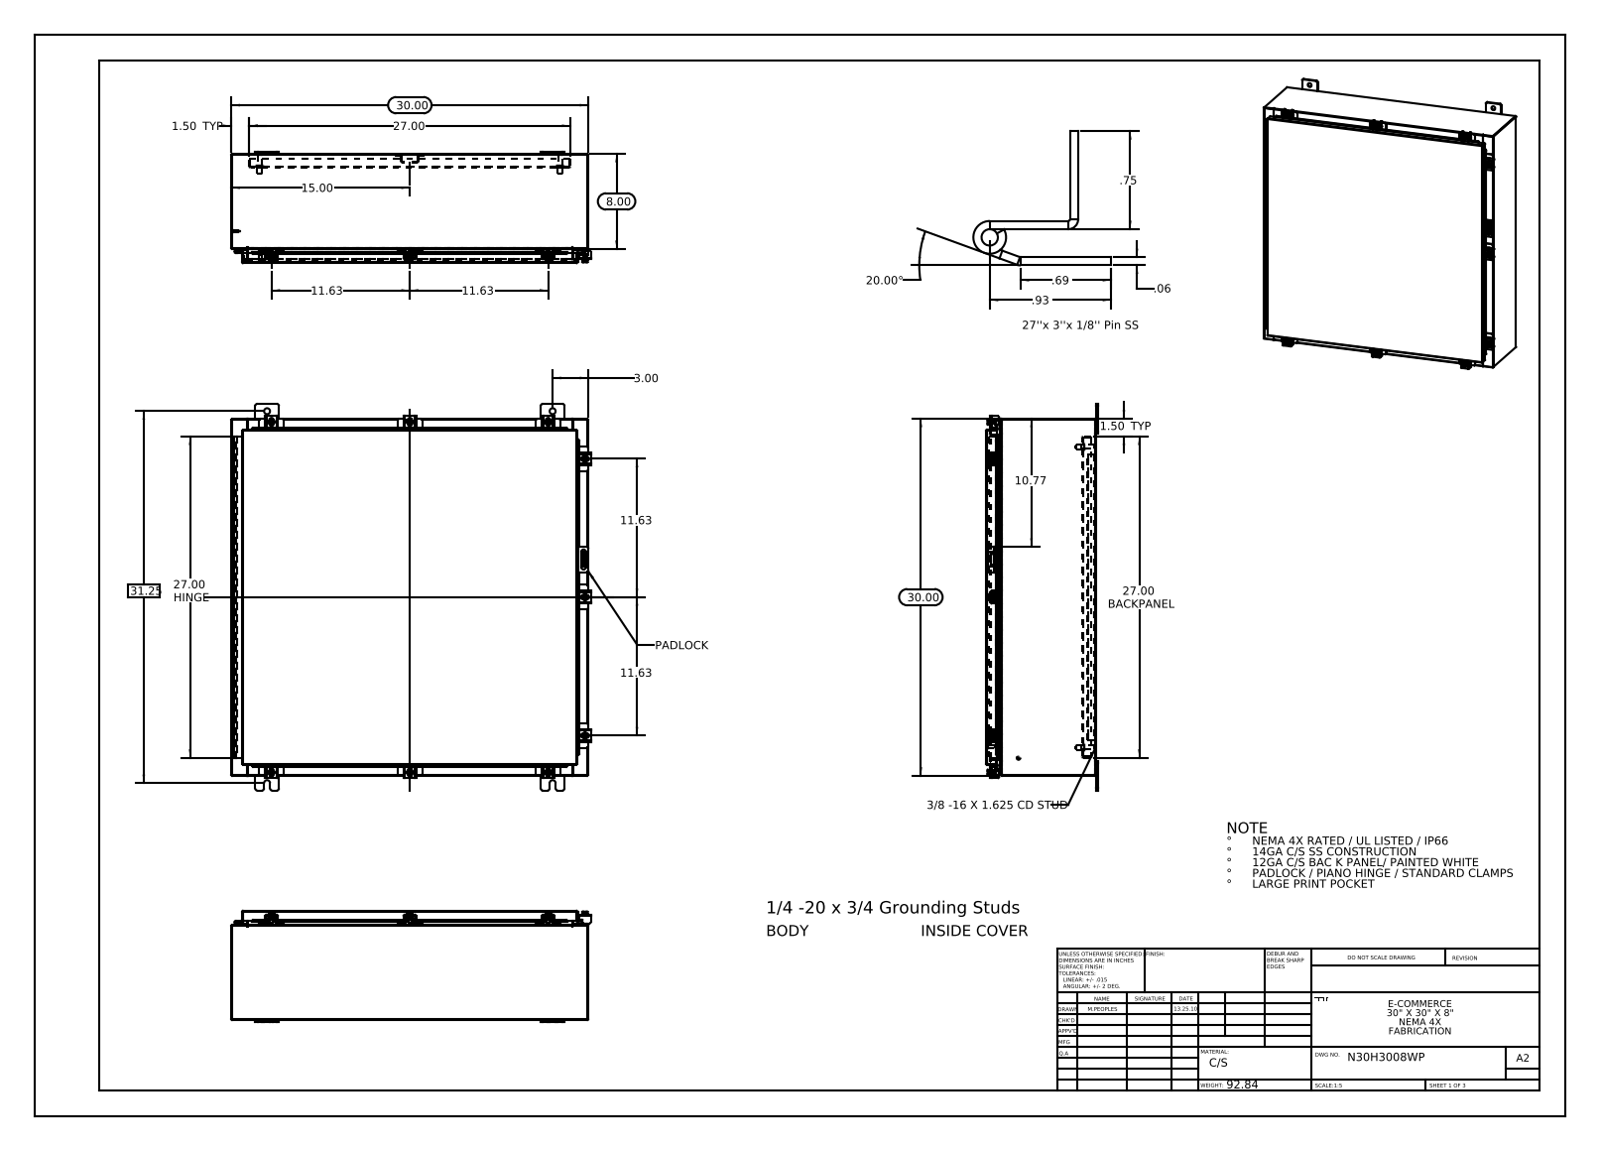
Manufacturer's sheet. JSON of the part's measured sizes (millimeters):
{"part_name": "N30H3008SSWP Clamp Bracket; N30H3008WP; N30H3008SSWP 22101002; N30H3008SSWP Body (+8 more)", "step_written_by": "SolidWorks 2013 (CONFIG_CONTROL_DESIGN)", "units": "millimeters", "bodies": {"solids": 65, "faces": 2288, "planar": 1212, "cylindrical": 944, "other": 132}, "overall_size": [825.5, 767.4, 238.5], "volume_mm3": 5342000, "surface_area_mm2": 5246000, "round_holes": [[5.4, 9], [6.6, 9], [12.7, 8], [3.2, 2]], "round_bosses_or_shafts": [[6.4, 10], [12.7, 9], [10.1, 9], [15.9, 4], [9.5, 4], [8.4, 4], [8, 2], [6, 2]], "partial_cylinders_radius": [[1.5, 42], [0.3, 31], [2.2, 25], [4.8, 24], [3, 18], [3.6, 18], [1.3, 13], [2, 12]], "face_to_face_distances": [1.9, 231.8, 760.1, 229.9, 233.7, 2.6, 206.4, 25.4, 27.3, 204.5], "hole_center_spacings": [59.1, 295.3, 325.1, 382.2, 695.2, 765.1, 804.2, 928.4]}
